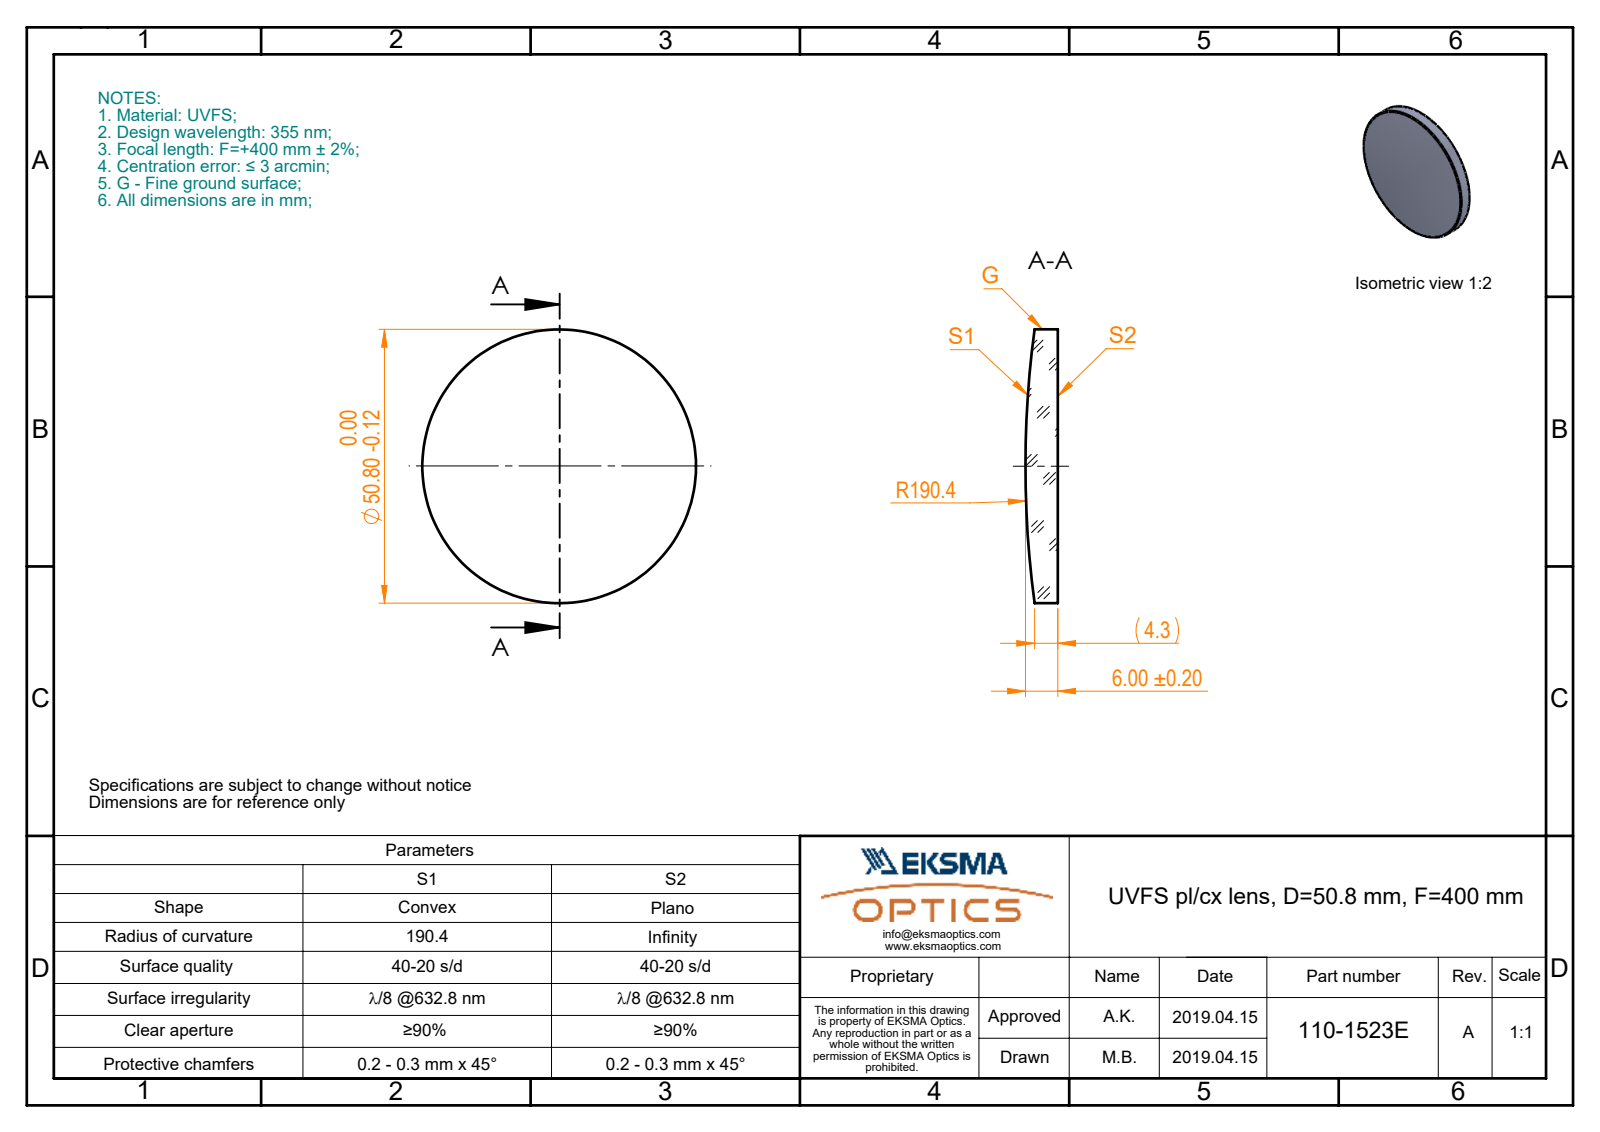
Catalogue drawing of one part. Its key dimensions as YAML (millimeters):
part_name: "110-1523E UVFS pl-cx 50.8 F400"
step_written_by: "SolidWorks 2017 (CONFIG_CONTROL_DESIGN)"
units: millimeters
bodies: {solids: 1, faces: 5, planar: 1, cylindrical: 2, other: 2}
overall_size: [50.8, 50.8, 6]
volume: 10439
surface_area: 4749
round_bosses_or_shafts:
  - {diameter: 50.8, count: 1}
